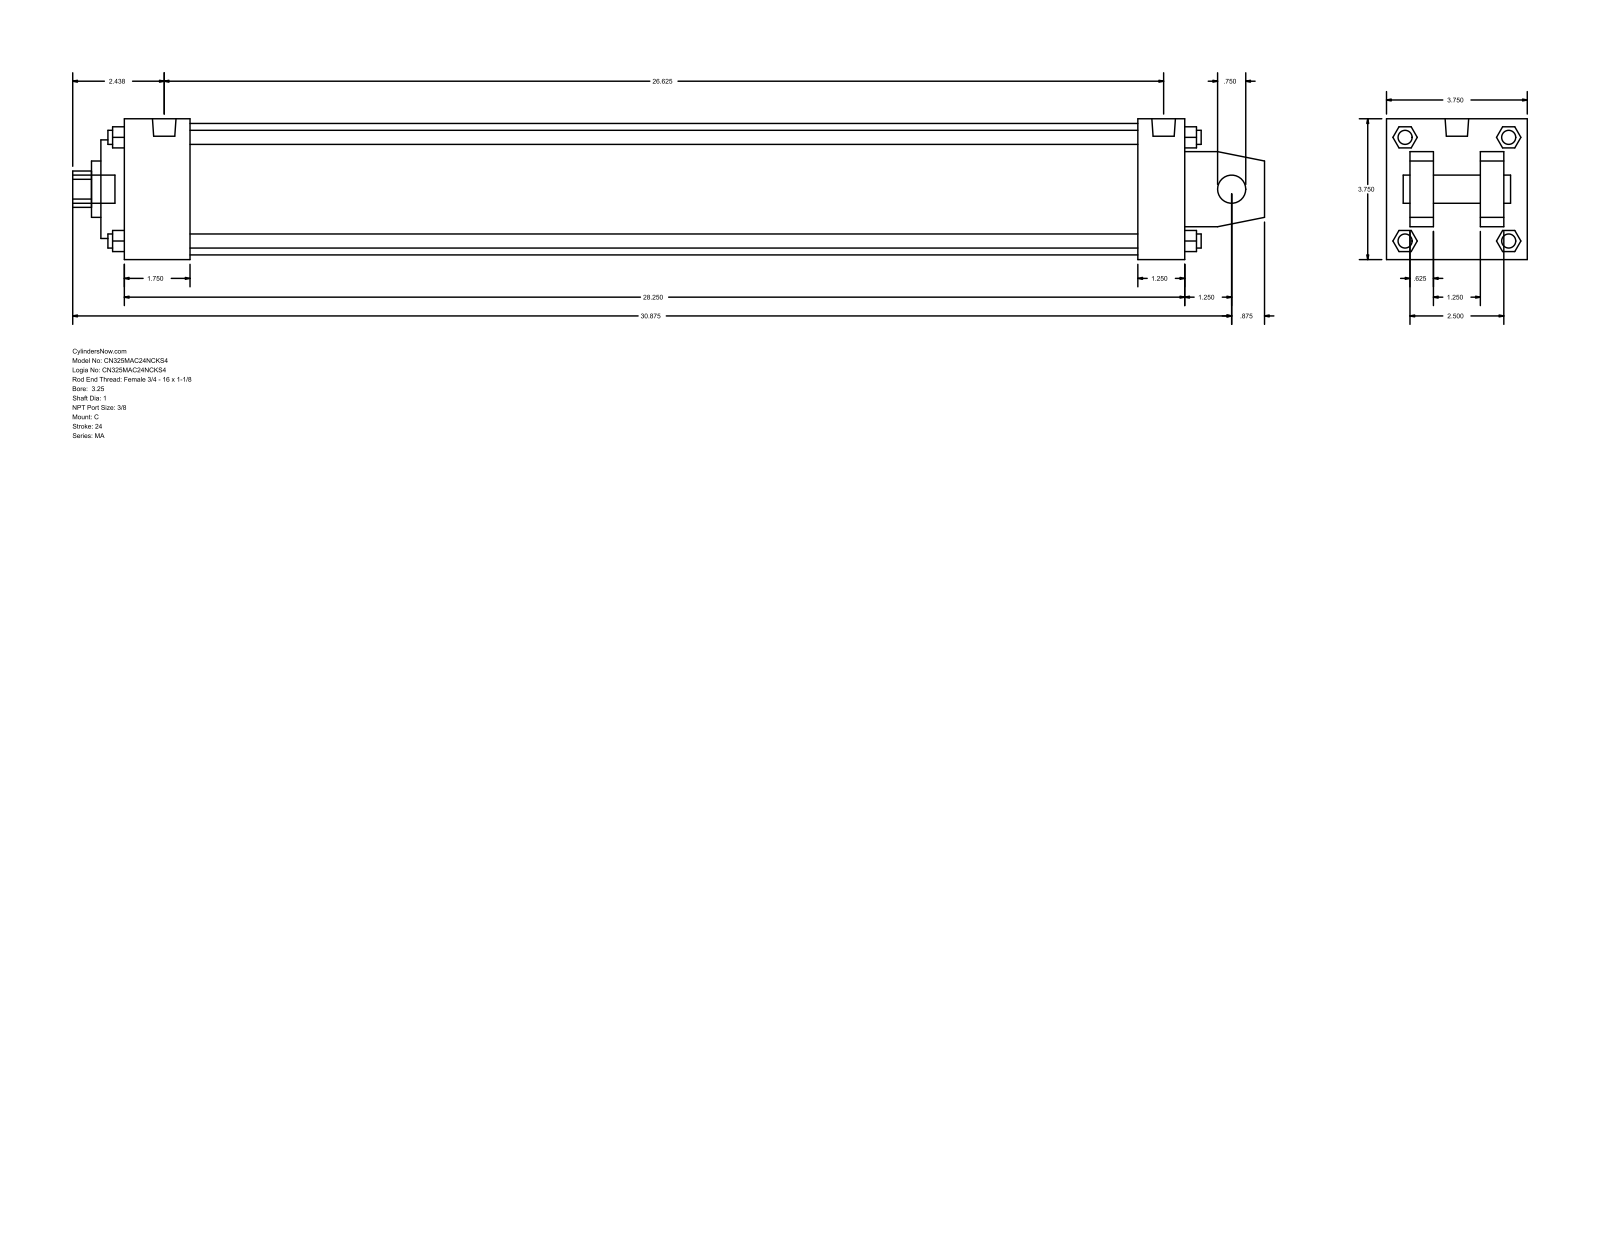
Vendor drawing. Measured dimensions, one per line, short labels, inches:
name: MA_C__0325_1
written by: GSSL Pune (CONFIG_CONTROL_DESIGN)
unit: in
bodies: 0 solids, 141 faces (109 planar, 32 cylindrical, 0 other)
size: 31.75 × 3.75 × 3.75
holes: 1× ⌀0.75, 1× ⌀1, 1× ⌀1.5, 1× ⌀2.625, 1× ⌀3.5
bosses: 4× ⌀0.437, 4× ⌀0.375, 2× ⌀0.627, 1× ⌀0.75
rounds: 1× R0.484
face distances: 3.75, 0.625, 2.5, 28.25, 1.25, 3.125, 1.875, 27, 1.25, 1.75
